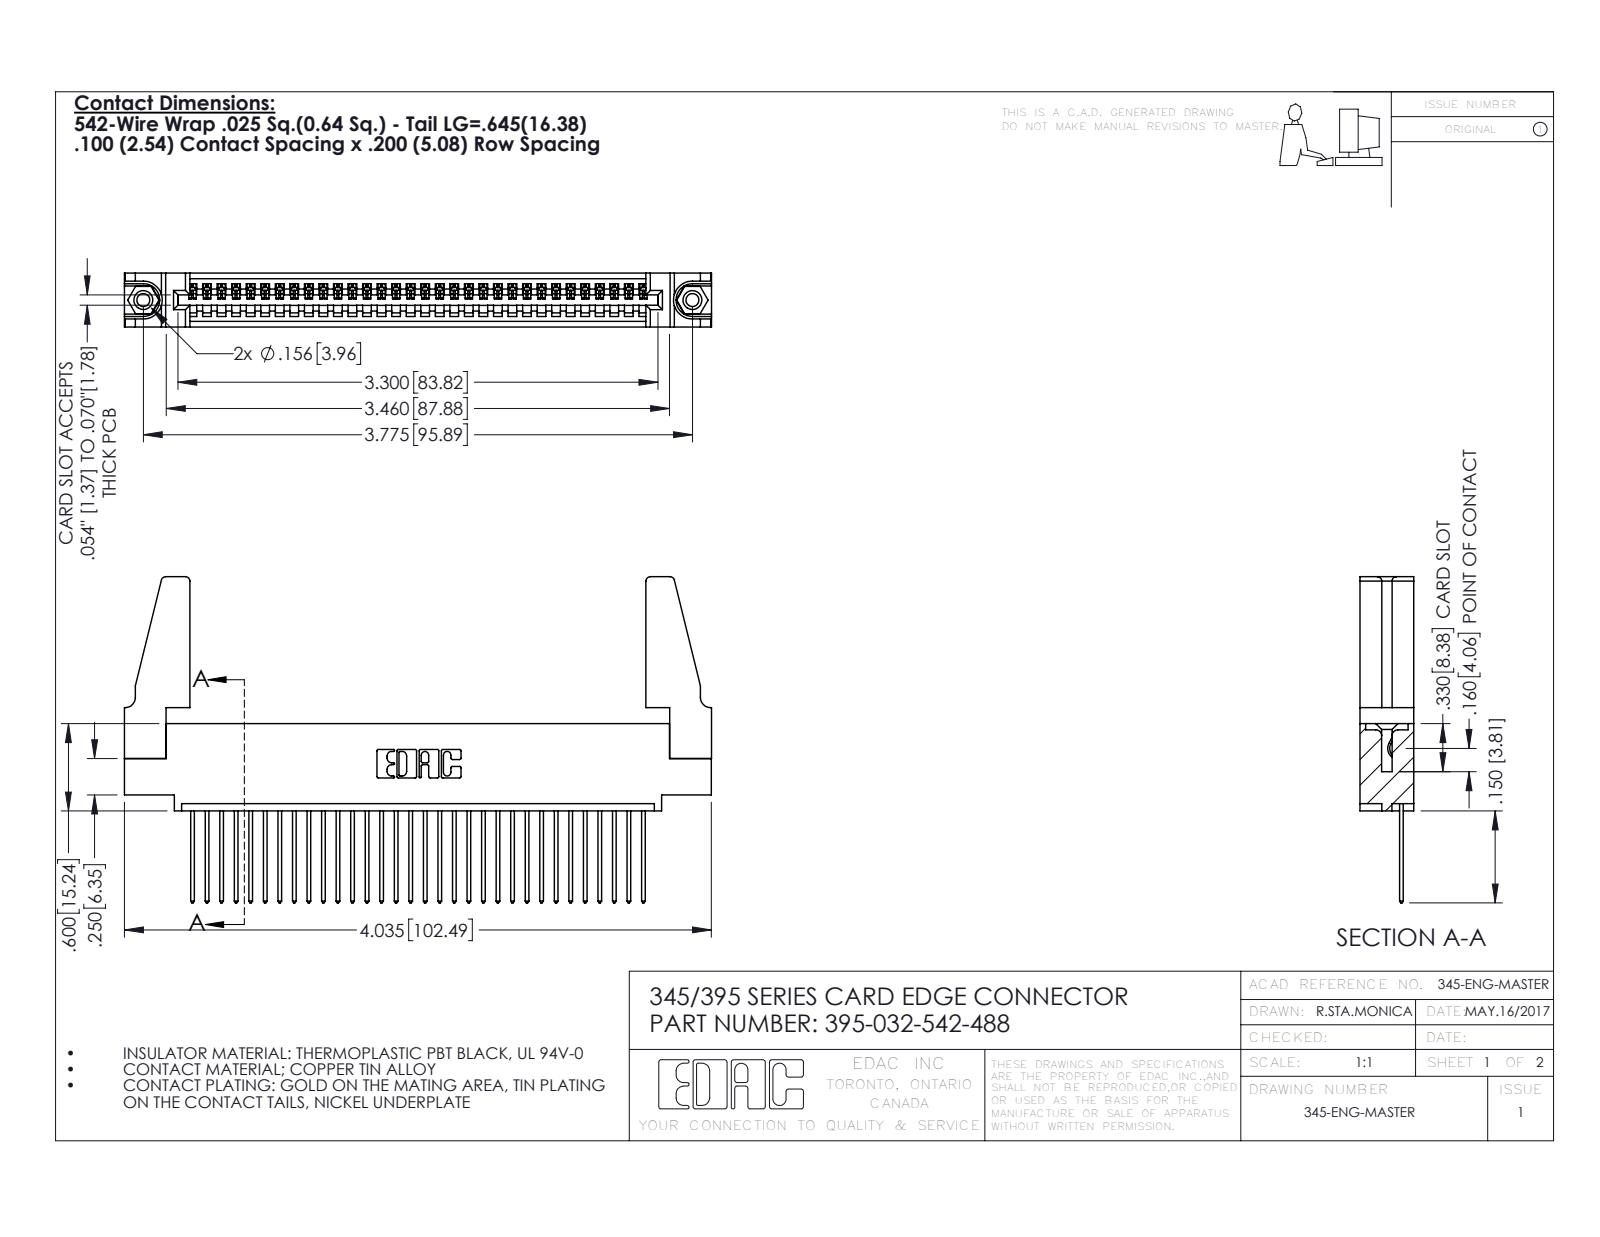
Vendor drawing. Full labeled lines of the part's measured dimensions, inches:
Part name (STEP PRODUCT): 395-032-542-488; 345-220-078_345-220-088; 345-250-001_345-250-001-102; 345-292-001_345-293-142 (+1 more)
STEP written by: SolidWorks 2016 (CONFIG_CONTROL_DESIGN)
Units: inches
Bodies: 37 solids, 2110 faces (1436 planar, 658 cylindrical, 16 other)
Overall size (bounding box): 4.036 × 2.242 × 0.37
Volume: 0.788 in³ · Surface area: 25.35 in²
Round holes (diameter × count): ⌀0.089 ×2, ⌀0.125 ×2, ⌀0.156 ×2, ⌀0.064 ×1
Round bosses / shafts (diameter × count): ⌀0.155 ×2
Partial cylindrical surfaces — rounded edges, fillets, slot ends (radius × count): R0.006 ×64, R0.01 ×64, R0.01 ×22, R0.03 ×8, R0.007 ×6, R0.031 ×6, R0.026 ×3, R0.031 ×2
Main face-to-face distances: 0.072, 0.298, 0.37, 0.098, 0.272, 0.025, 0.2, 0.225, 0.149, 0.072
Hole centre spacings: 0.27, 3.54, 3.775
